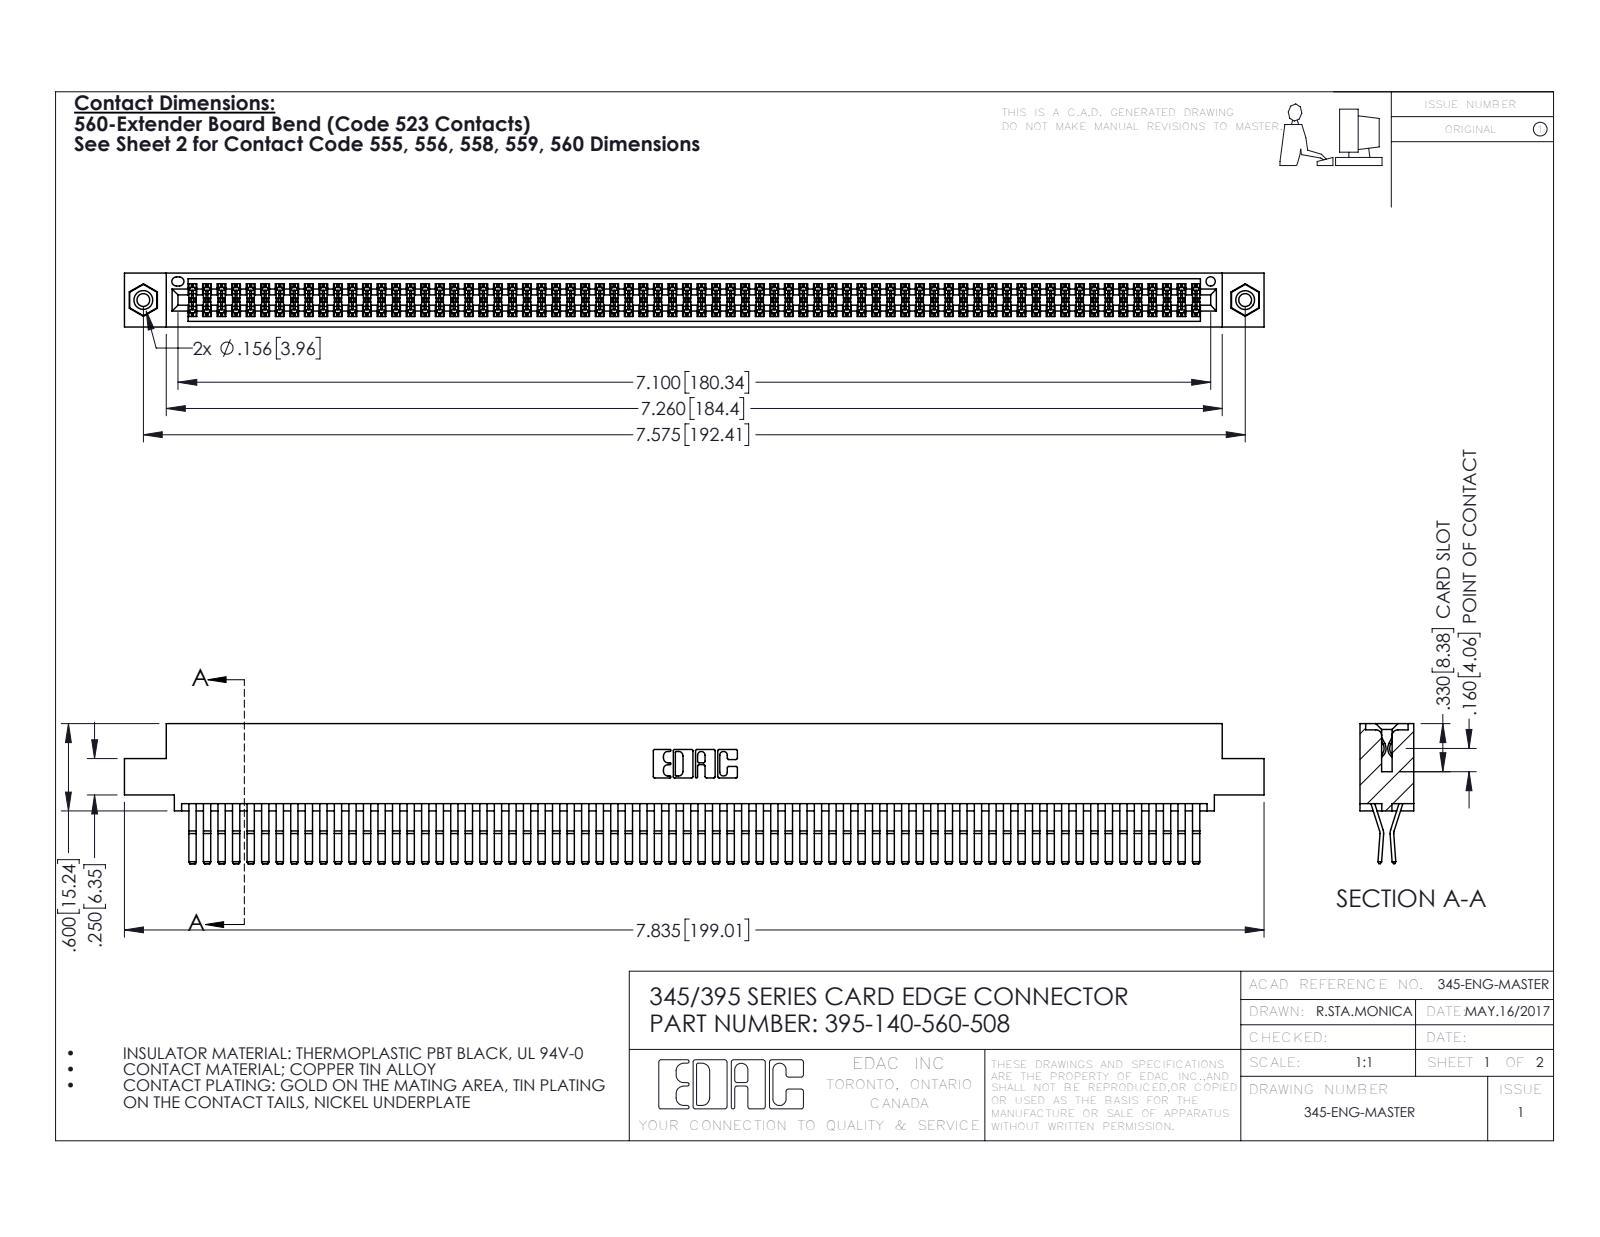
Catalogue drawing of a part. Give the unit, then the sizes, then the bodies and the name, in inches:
Units: inches
Overall size (bounding box): 7.835 × 0.962 × 0.37
Round holes (diameter × count): ⌀0.089 ×2, ⌀0.125 ×2, ⌀0.156 ×2, ⌀0.064 ×1
Round bosses / shafts (diameter × count): ⌀0.155 ×2
Partial cylindrical surfaces — rounded edges, fillets, slot ends (radius × count): R0.006 ×210, R0.01 ×22, R0.007 ×6, R0.031 ×6, R0.026 ×3, R0.01 ×2, R0.014 ×2, R0.019 ×2
Main face-to-face distances: 0.025, 0.072, 0.298, 0.37, 0.2, 0.098, 0.272, 0.225, 0.175, 0.149
Hole centre spacings: 0.27, 7.339, 7.575
Volume: 1.247 in³ · Surface area: 51.47 in²
Bodies: 143 solids, 7470 faces (4736 planar, 2718 cylindrical, 16 other)
Part name (STEP PRODUCT): 345-292-001_560 Tail; 345-250-001_345-250-003-102; 345 Part_0.110 Offset - 0.156 Dia-TI; 395-140-560-508
STEP written by: SolidWorks 2016 (CONFIG_CONTROL_DESIGN)
